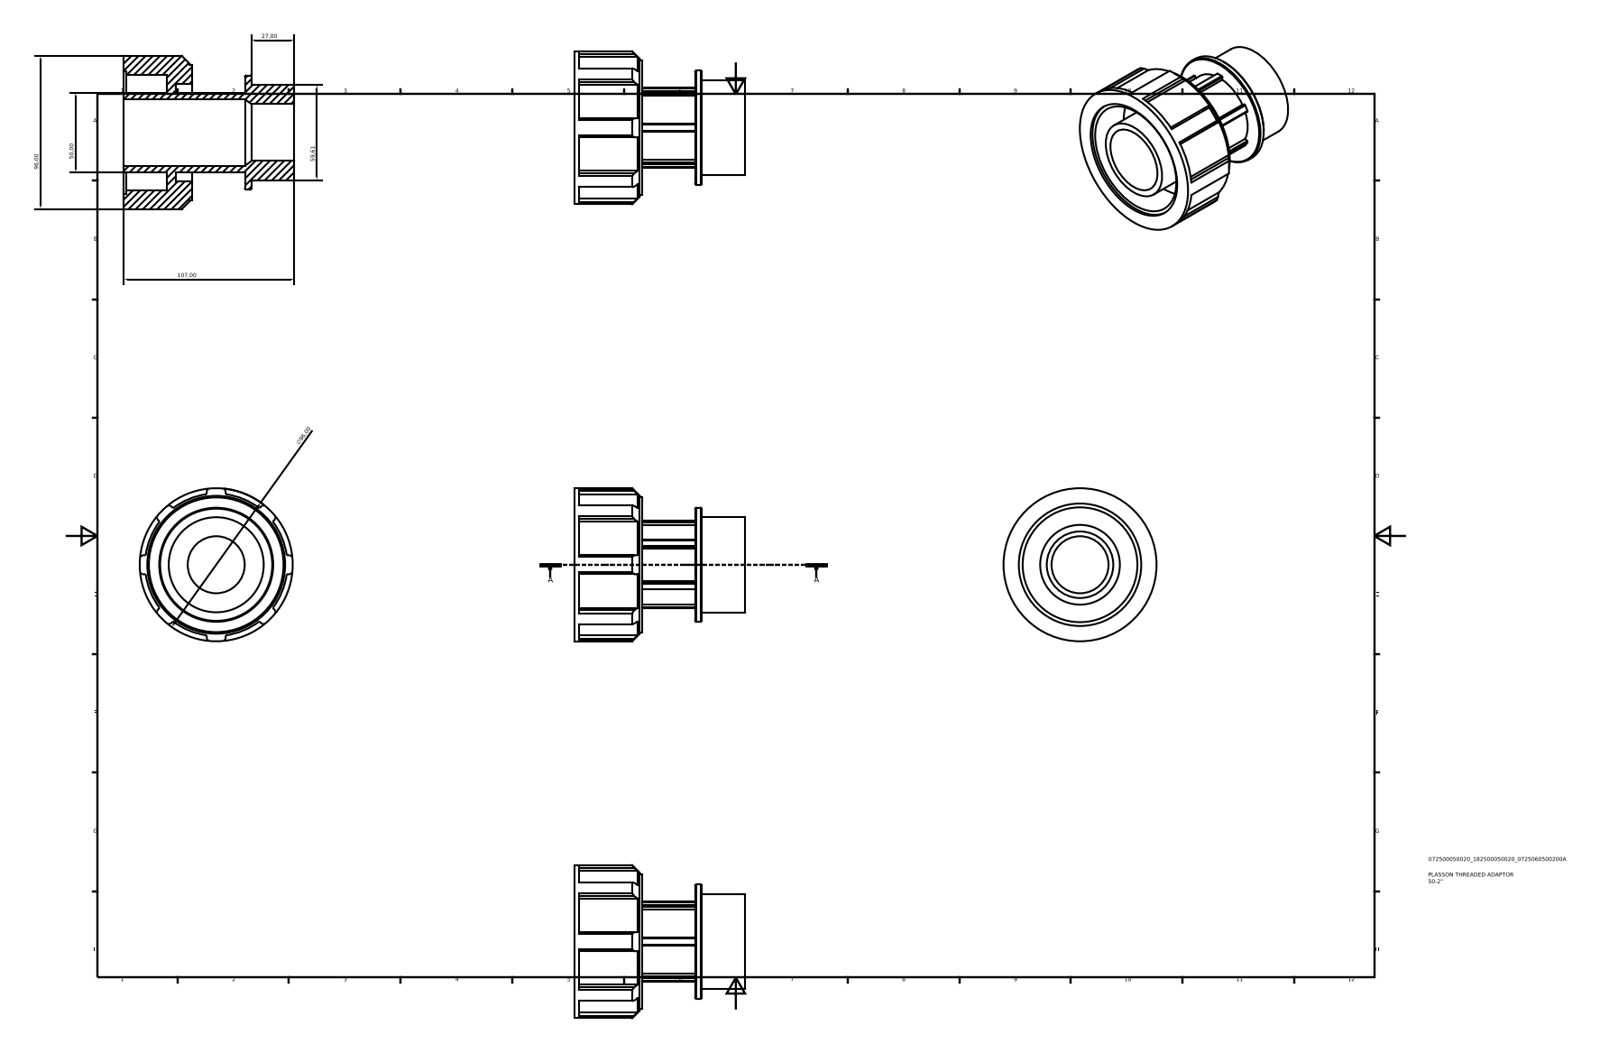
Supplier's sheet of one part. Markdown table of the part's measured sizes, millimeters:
| quantity | value |
| --- | --- |
| part name | 072500050020_182500050020 |
| STEP written by | Autodesk Inventor 2015 (AUTOMOTIVE_DESIGN) |
| units | millimeters |
| bodies | 1 solid, 108 faces (74 planar, 30 cylindrical, 4 other) |
| overall size | 107 × 96 × 96 |
| volume | 236 836 mm³ |
| surface area | 69 030 mm² |
| round holes (diameter × count) | 35.77 × 1, 41.73 × 1, 61 × 1, 72 × 1, 76.8 × 1 |
| round bosses / shafts (diameter × count) | 96 × 1, 84.48 × 1, 71.54 × 1, 59.61 × 1, 50 × 1 |
| partial cylindrical surfaces (radius × count) | 27.5 × 1, 44.64 × 1 |
| main face-to-face distances | 27, 80, 42.8, 15.8, 75.95, 48.95, 33.15, 107, 64.2, 31.05 |
